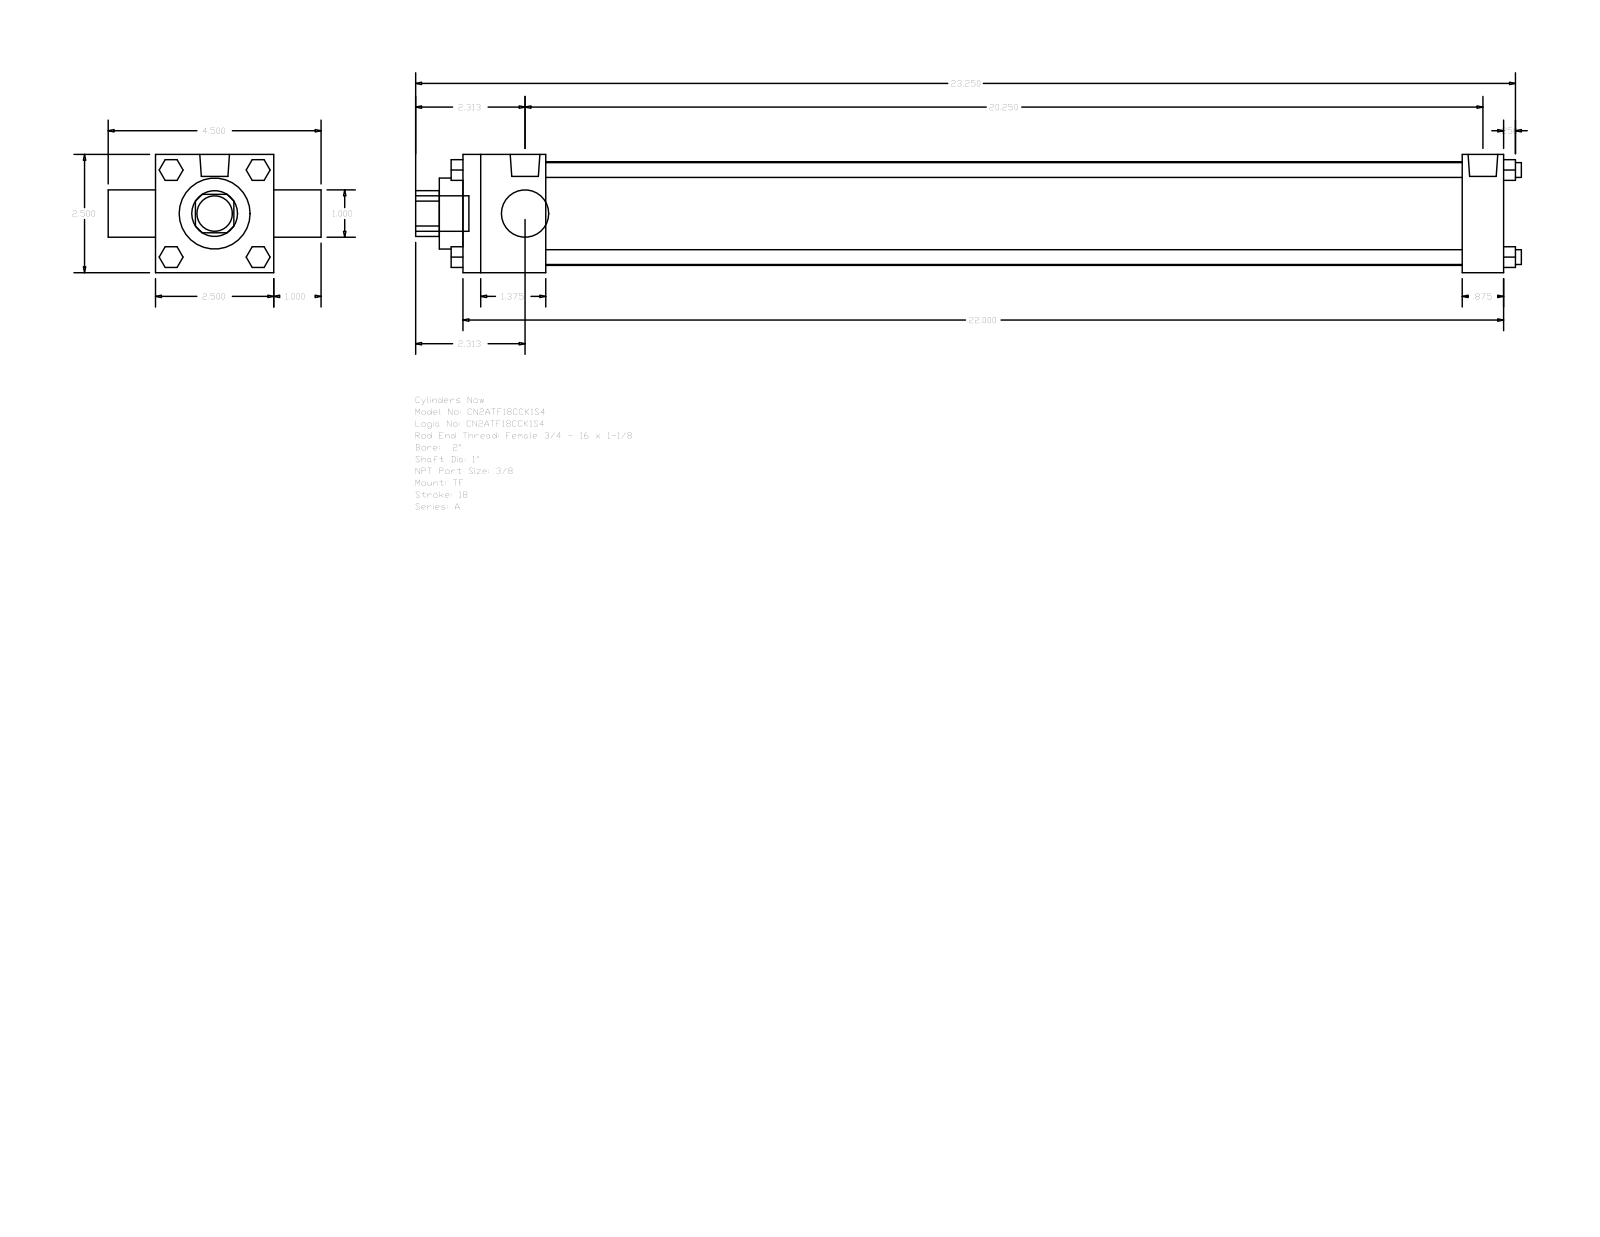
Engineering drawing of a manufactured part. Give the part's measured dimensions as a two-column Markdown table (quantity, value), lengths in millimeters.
| quantity | value |
| --- | --- |
| part name | A_TF__0200_1 |
| STEP written by | GSSL Pune (CONFIG_CONTROL_DESIGN) |
| units | millimeters |
| bodies | 0 solids, 120 faces (92 planar, 28 cylindrical, 0 other) |
| overall size | 593.73 × 114.3 × 63.5 |
| round holes (diameter × count) | 25.4 × 2, 38.1 × 1, 55.63 × 1 |
| round bosses / shafts (diameter × count) | 7.94 × 4, 5.56 × 3, 15.93 × 2, 19.05 × 1 |
| partial cylindrical surfaces (radius × count) | 12.29 × 1 |
| main face-to-face distances | 63.5, 558.8, 44.45, 536.58, 492.13, 514.35, 22.22, 25.4, 88.9, 571.5 |
